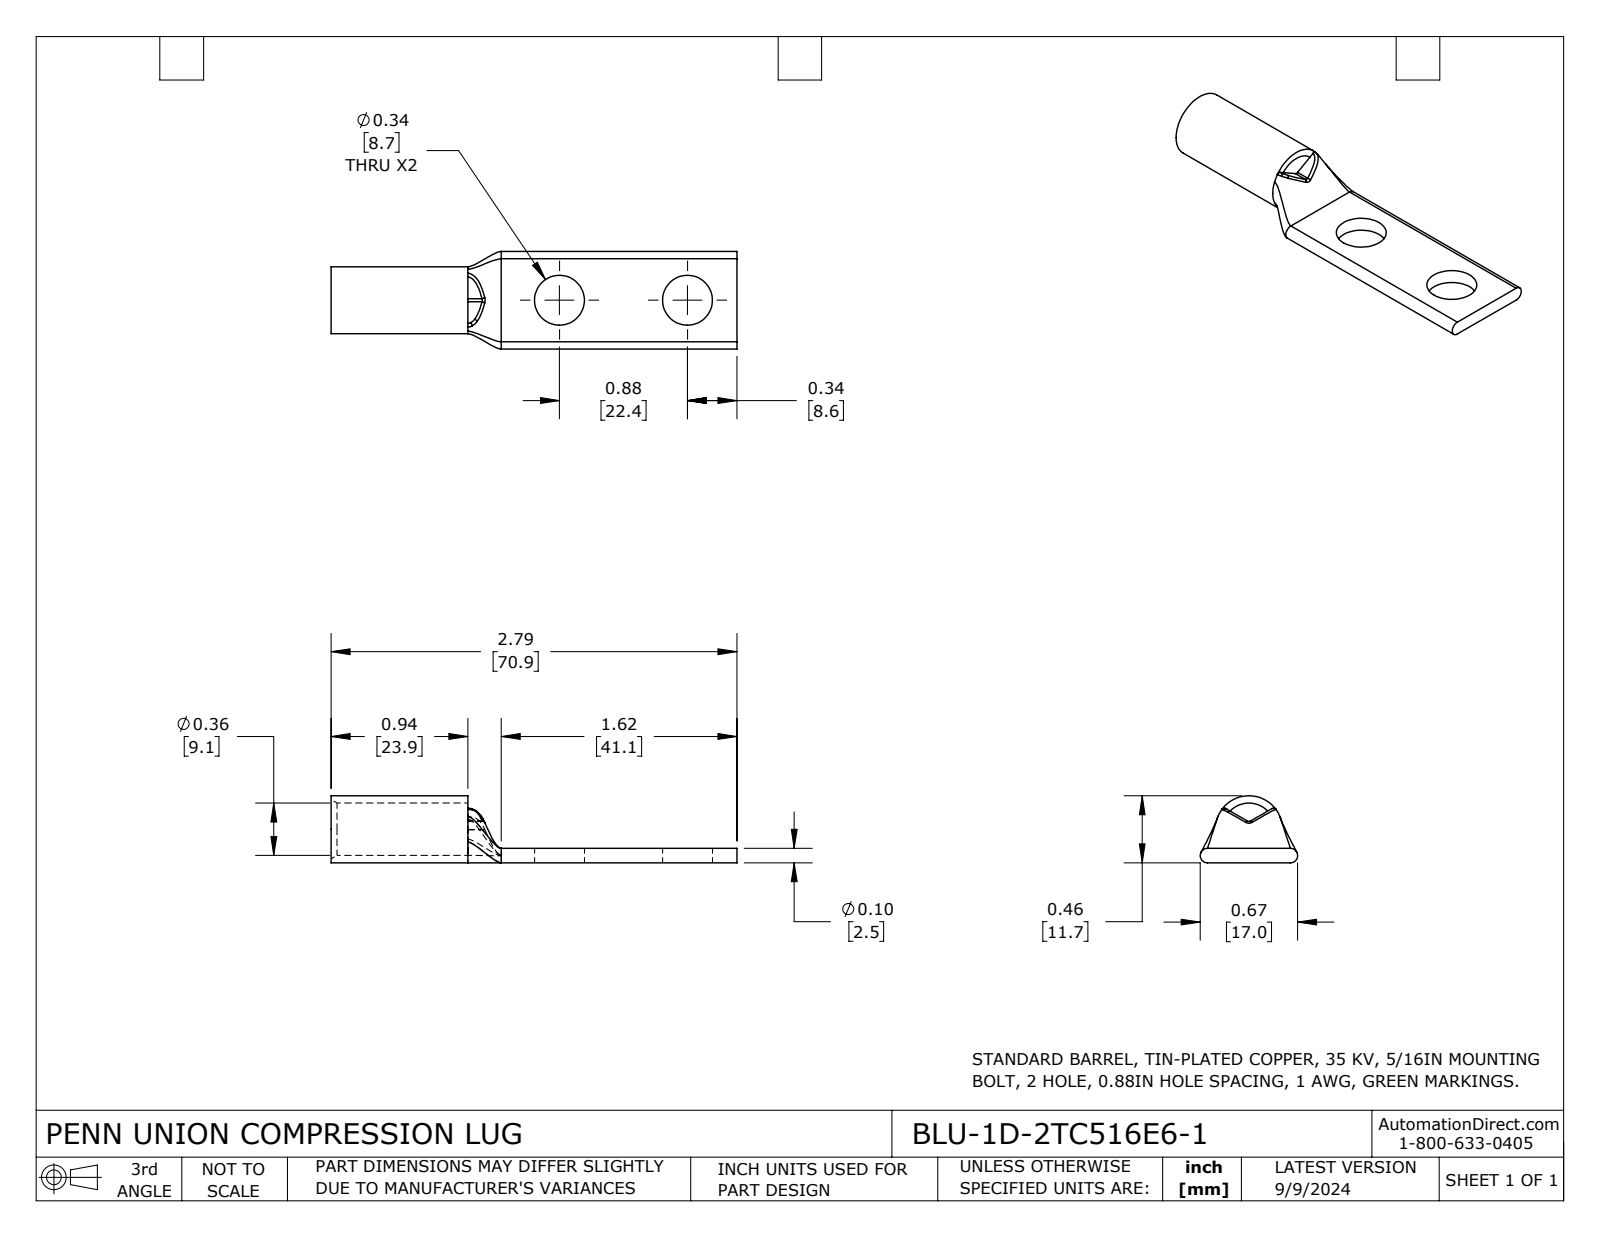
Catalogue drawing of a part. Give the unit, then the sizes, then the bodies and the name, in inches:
Units: inches
Overall size (bounding box): 2.79 × 0.67 × 0.461
Round holes (diameter × count): ⌀0.343 ×2, ⌀0.36 ×1
Round bosses / shafts (diameter × count): ⌀0.461 ×1
Partial cylindrical surfaces — rounded edges, fillets, slot ends (radius × count): R0.02 ×2, R0.05 ×2
Main face-to-face distances: 0.1, 2.79, 0.94, 1.85, 0.05, 1.17, 0.23, 1.62
Hole centre spacings: 0.88
Volume: 0.161 in³ · Surface area: 5.494 in²
Bodies: 1 solid, 39 faces (11 planar, 13 cylindrical, 15 other)
Part name (STEP PRODUCT): BLU-1D-2TC516E6-1
STEP written by: SolidWorks 2023 (CONFIG_CONTROL_DESIGN)
